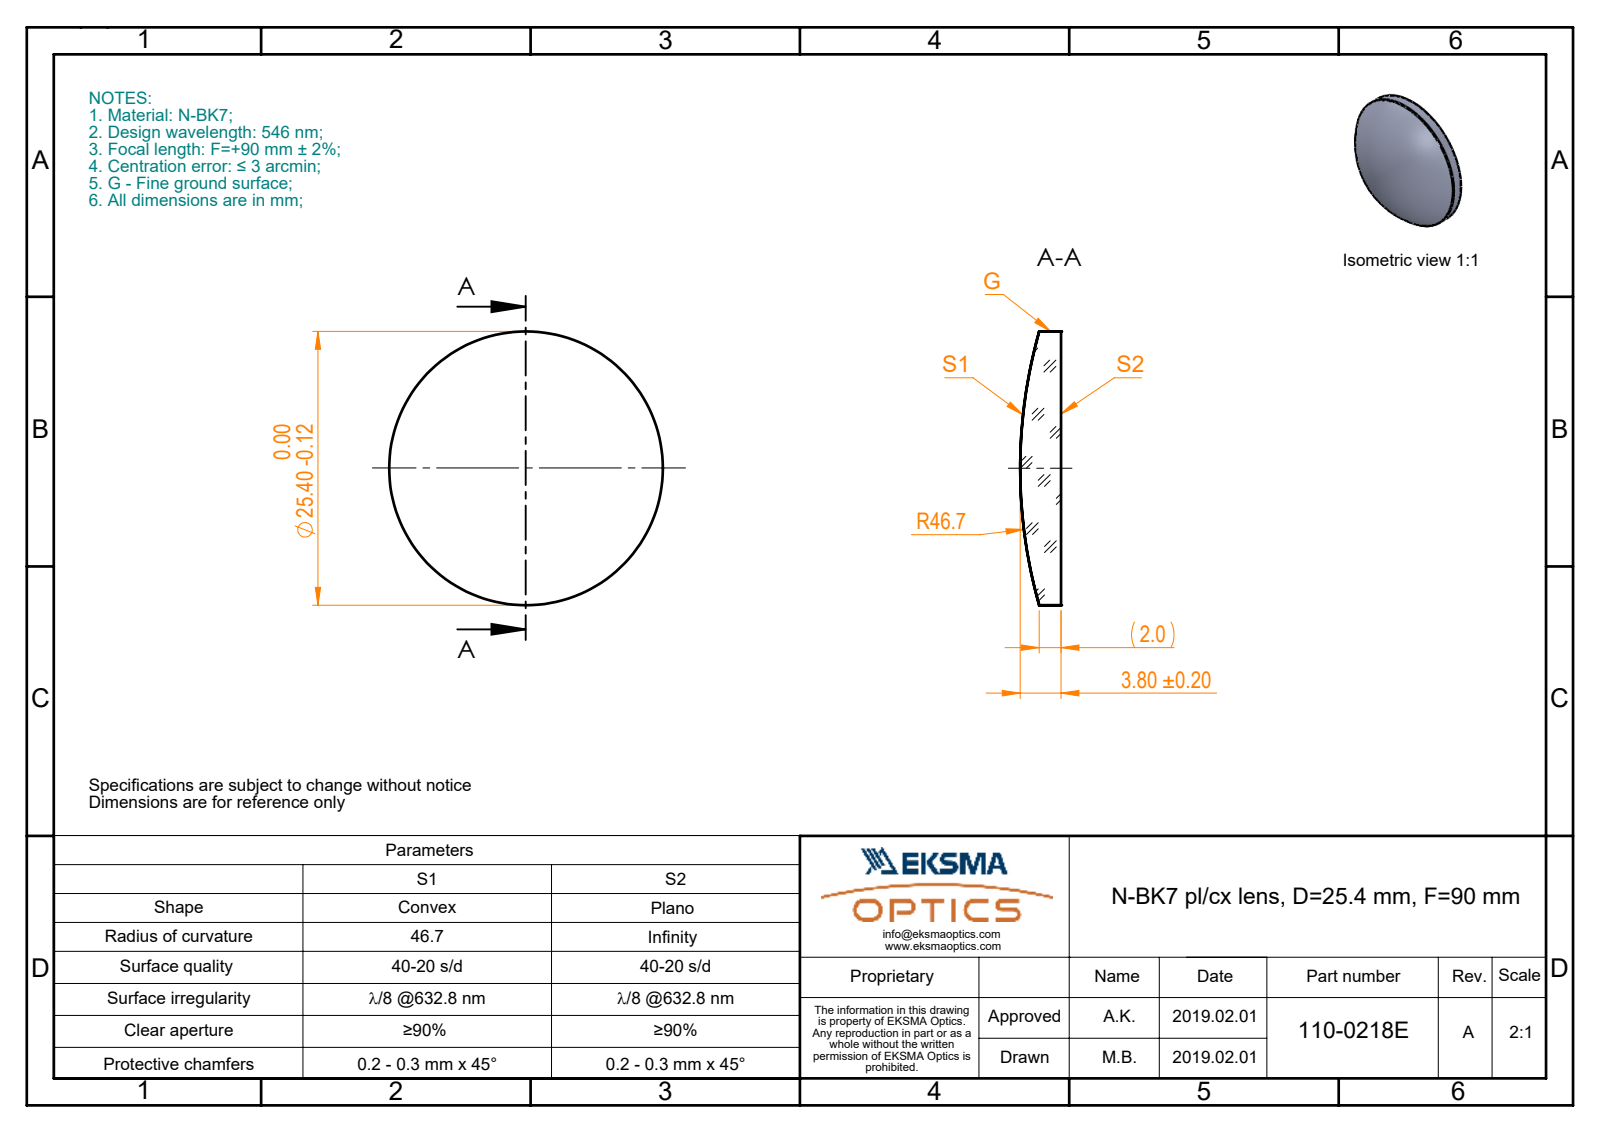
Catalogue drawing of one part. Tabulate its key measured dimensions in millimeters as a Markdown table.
| quantity | value |
| --- | --- |
| part name | 110-0218E BK7 pl-cx 25.4 F90 |
| STEP written by | SolidWorks 2017 (CONFIG_CONTROL_DESIGN) |
| units | millimeters |
| bodies | 1 solid, 5 faces (1 planar, 2 cylindrical, 2 other) |
| overall size | 25.4 × 25.4 × 3.8 |
| volume | 1 482 mm³ |
| surface area | 1 186 mm² |
| round bosses / shafts (diameter × count) | 25.4 × 1 |
